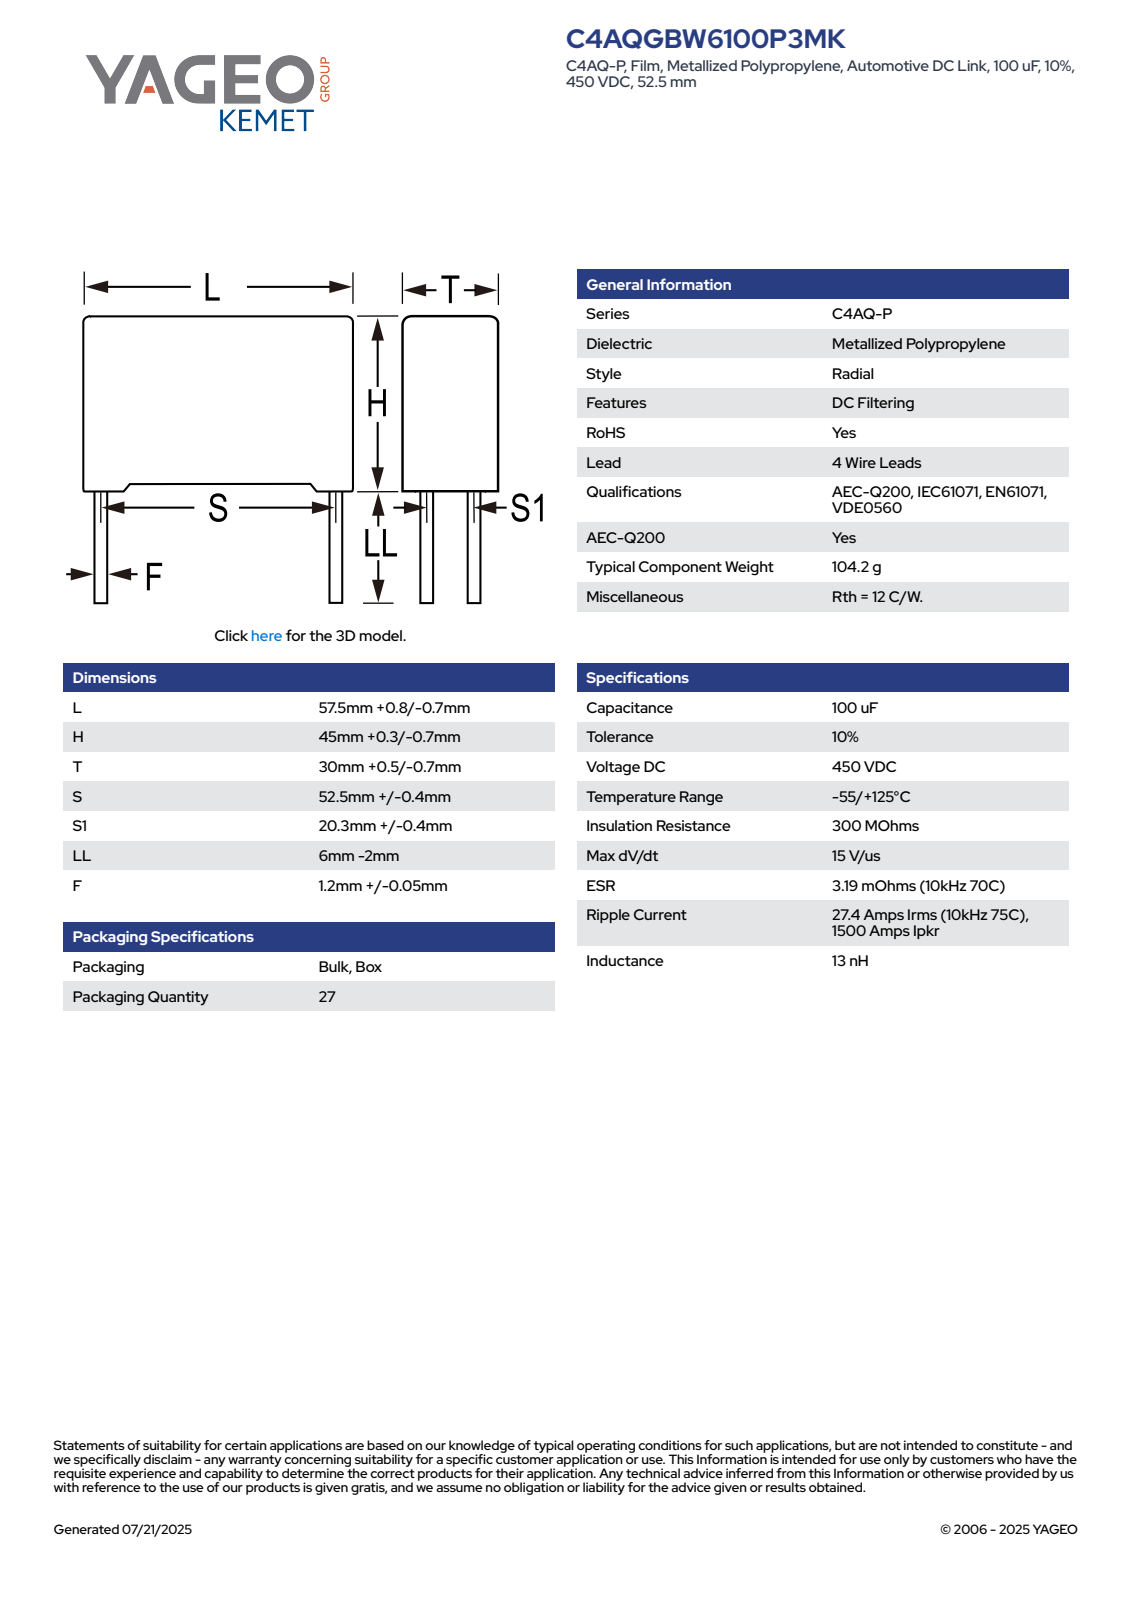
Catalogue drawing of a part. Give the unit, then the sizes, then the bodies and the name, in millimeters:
Units: millimetres
Overall size (bounding box): 58.3 × 49.3 × 30.5
Round bosses / shafts (diameter × count): ⌀1.25 ×4
Main face-to-face distances: 30.5, 43.97, 58.3, 1.33, 45.3, 30.51, 1.87, 56.43, 54.56, 28.63
Volume: 78 420 mm³ · Surface area: 11 899 mm²
Bodies: 4 solids, 87 faces (79 planar, 8 cylindrical, 0 other)
Part name (STEP PRODUCT): CFP_RB4_57.5X45X30_L58.3H45.3T30.5S52.5S120.3LL4F1.25
STEP written by: SolidWorks 2014 (AUTOMOTIVE_DESIGN)
